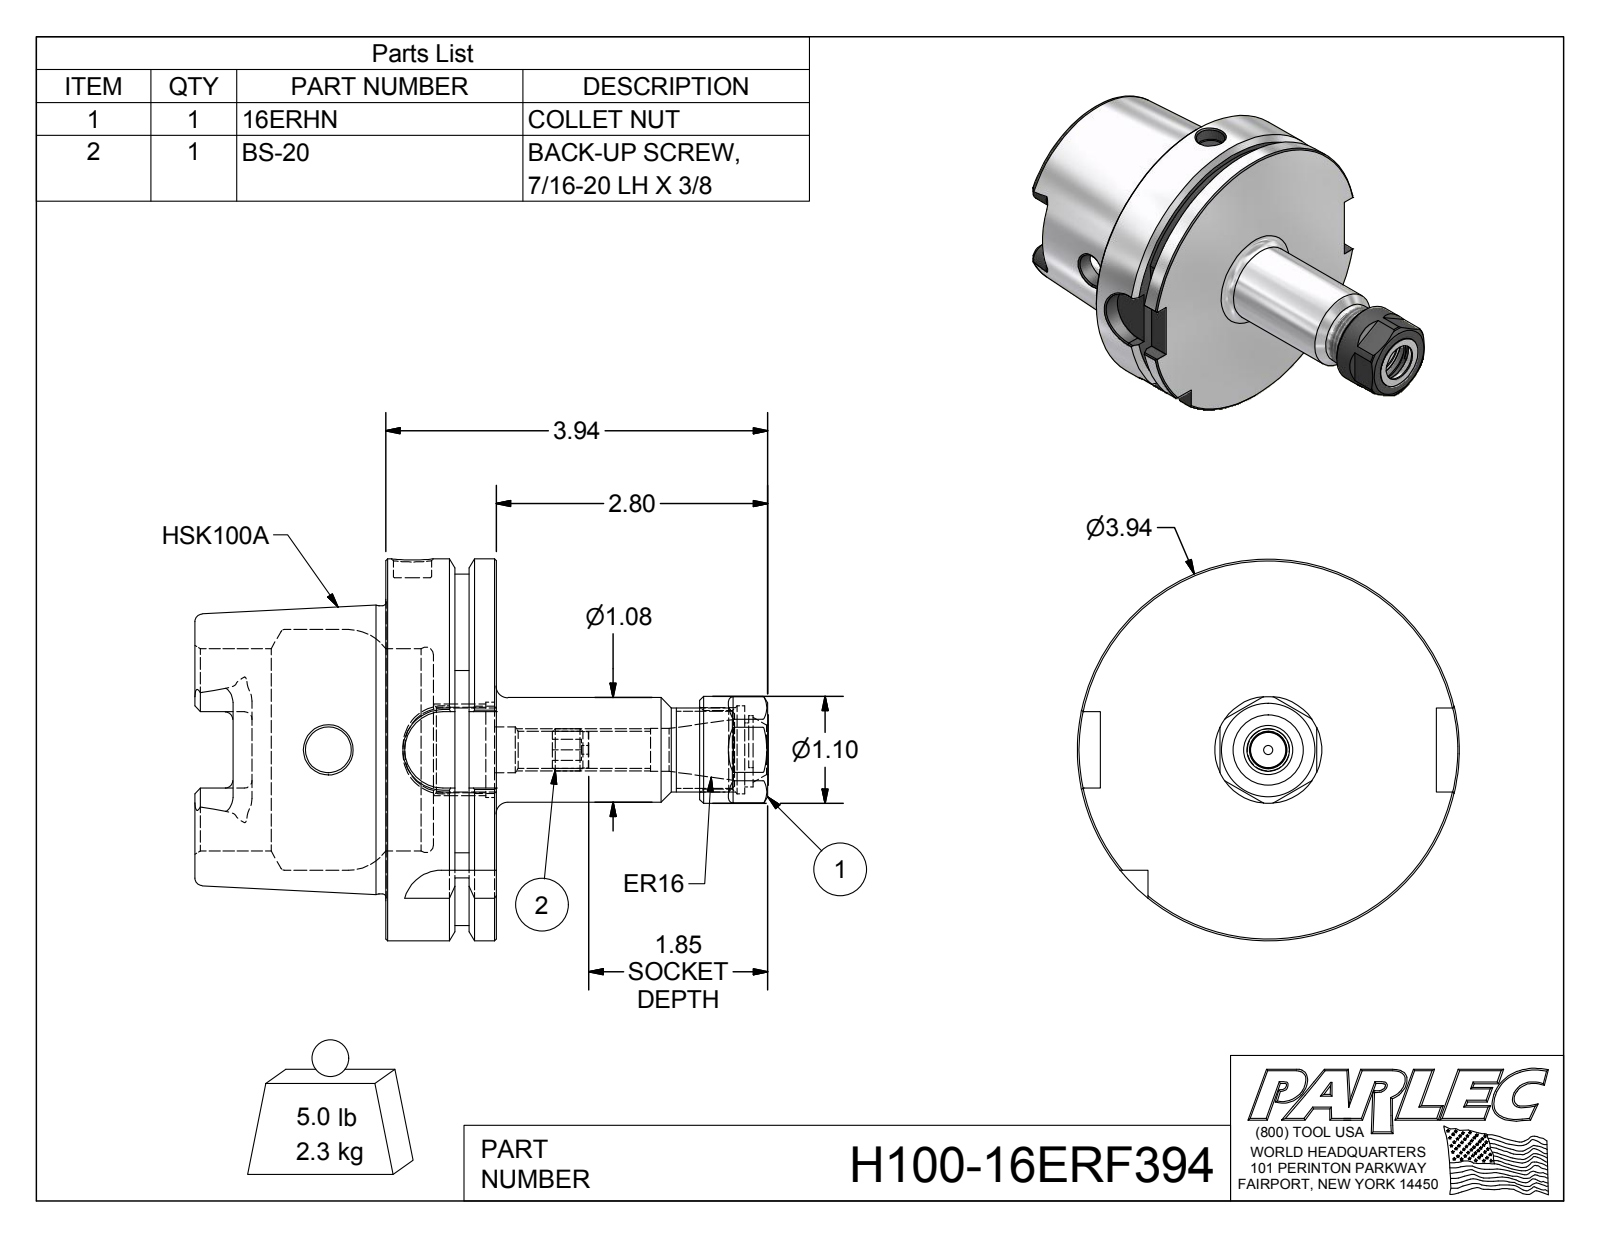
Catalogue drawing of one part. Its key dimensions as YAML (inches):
part_name: "H100-16ER4-1; 16ERHN; BS-20; H100-16ERF394"
step_written_by: "Autodesk Inventor 2016 (AUTOMOTIVE_DESIGN)"
units: inches
bodies: {solids: 3, faces: 184, planar: 68, cylindrical: 48, other: 68}
overall_size: [5.909, 3.937, 3.937]
volume: 17.47
surface_area: 94.47
round_holes:
  - {diameter: 0.354, count: 2}
  - {diameter: 0.472, count: 2}
  - {diameter: 0.09, count: 1}
  - {diameter: 0.383, count: 1}
  - {diameter: 0.394, count: 1}
  - {diameter: 0.44, count: 1}
  - {diameter: 0.472, count: 1}
  - {diameter: 0.488, count: 1}
  - {diameter: 0.67, count: 1}
  - {diameter: 0.807, count: 1}
  - {diameter: 0.881, count: 1}
  - {diameter: 0.906, count: 1}
round_bosses_or_shafts:
  - {diameter: 3.937, count: 1}
  - {diameter: 3.622, count: 1}
  - {diameter: 2.967, count: 1}
  - {diameter: 1.102, count: 1}
  - {diameter: 1.08, count: 1}
  - {diameter: 0.866, count: 1}
  - {diameter: 0.432, count: 1}
  - {diameter: 0.372, count: 1}
partial_cylinders:
  - {radius: 0.079, count: 6}
  - {radius: 0.192, count: 4}
  - {radius: 0.394, count: 4}
  - {radius: 0.285, count: 1}
  - {radius: 0.354, count: 1}
face_to_face_distances: [1.142, 0.492, 0.65, 1.969, 2.461, 3.11, 3.465, 2.83, 0.861, 0.369]
hole_center_spacings: [0.06]
